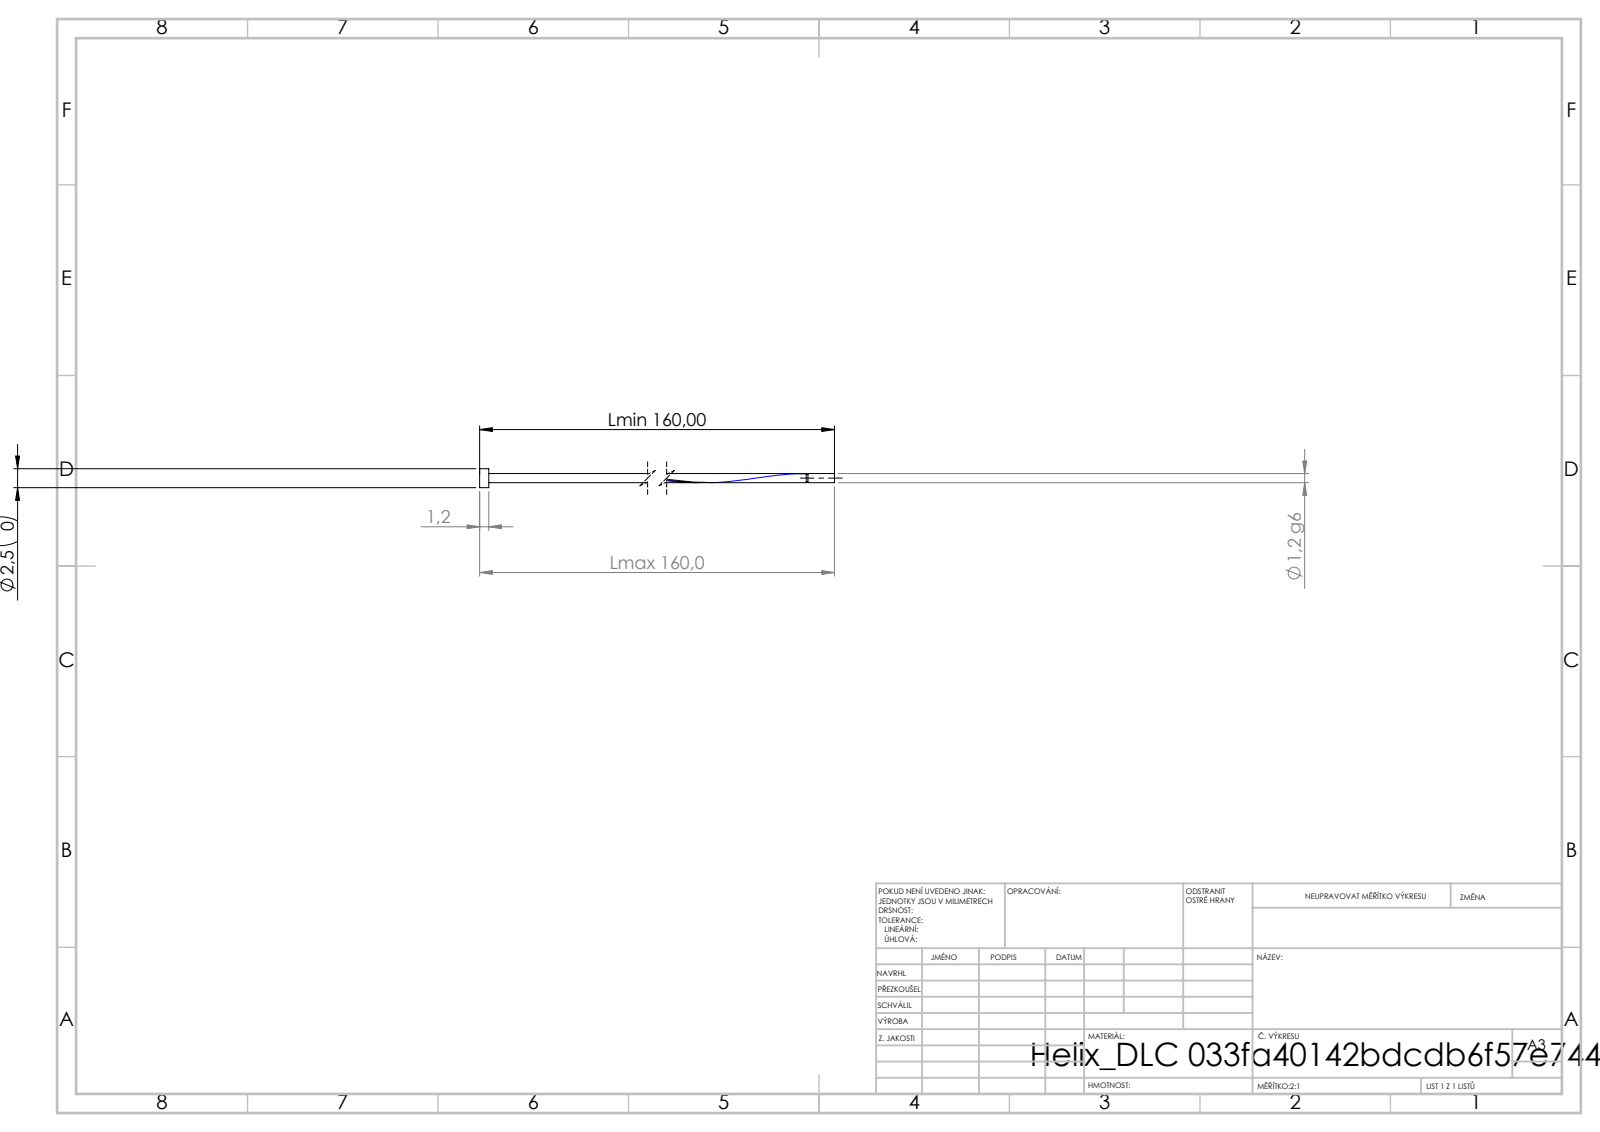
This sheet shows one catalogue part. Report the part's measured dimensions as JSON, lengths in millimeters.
{"step_written_by": "SolidWorks 2019 (CONFIG_CONTROL_DESIGN)", "units": "millimeters", "bodies": {"solids": 1, "faces": 16, "planar": 6, "cylindrical": 9, "other": 1}, "overall_size": [160, 2.5, 2.5], "volume_mm3": 224, "surface_area_mm2": 829, "round_bosses_or_shafts": [[2.5, 1], [1.2, 1], [0.96, 1]], "face_to_face_distances": [1.2, 160, 158.8, 156.53, 155.33, 3.47, 156.29, 155.09, 3.71, 76.29]}
